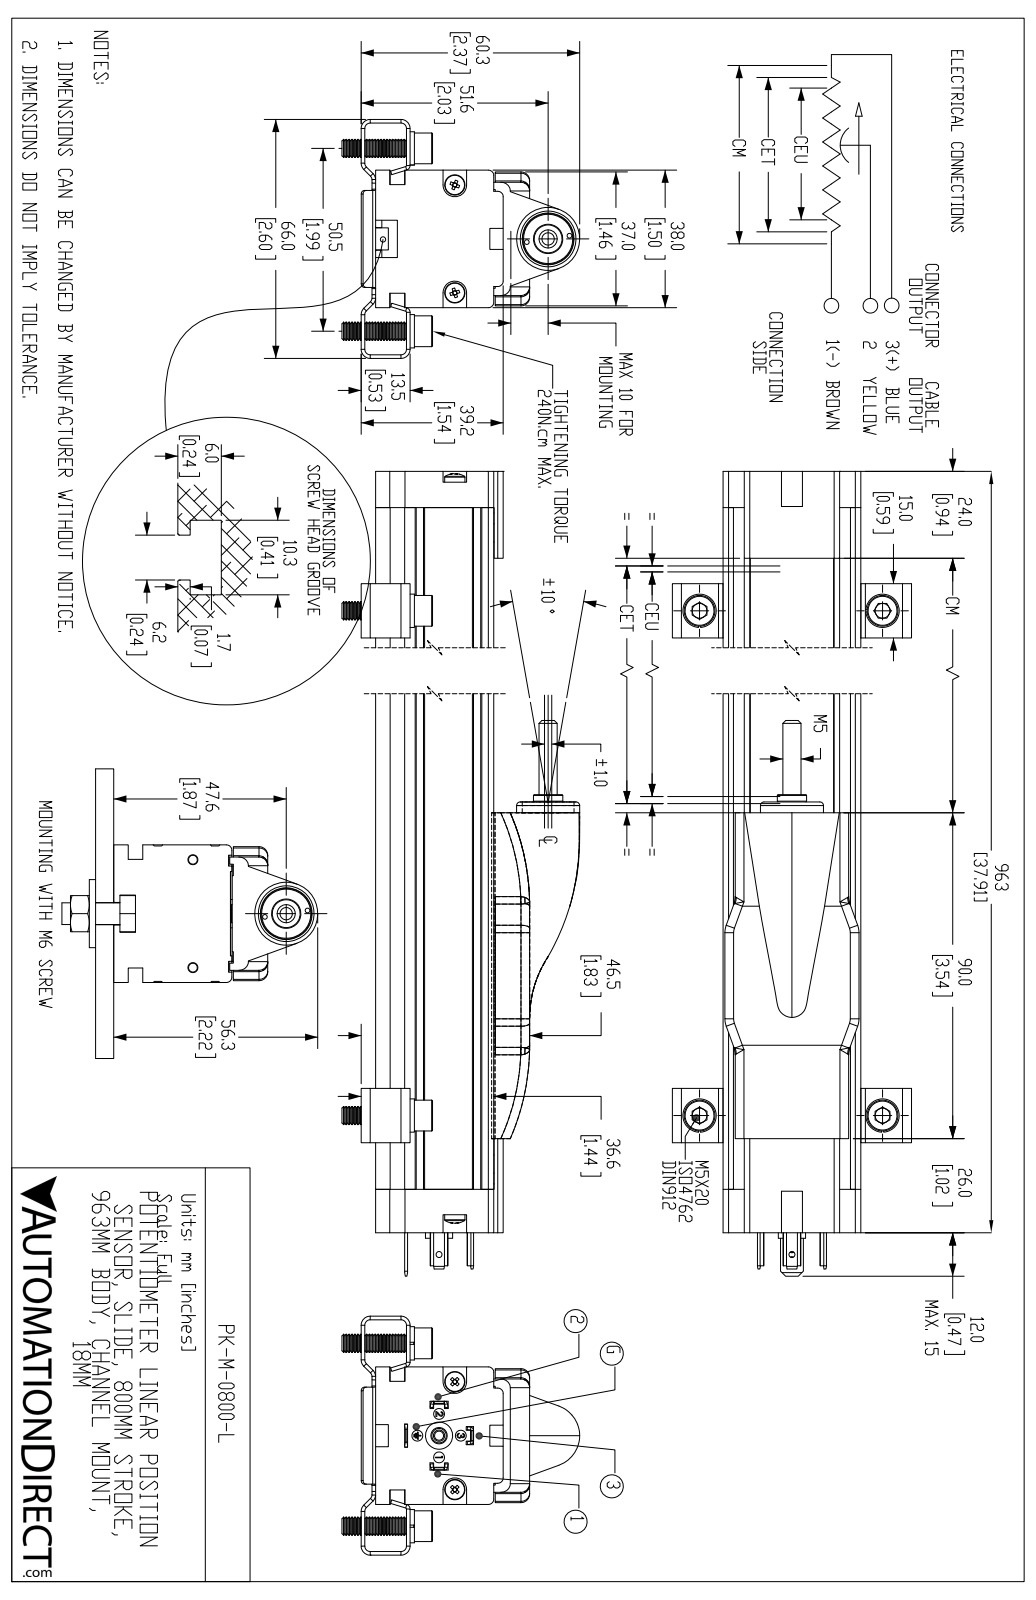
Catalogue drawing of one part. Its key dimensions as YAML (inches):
part_name: "PK-M-0800-L"
step_written_by: "SolidWorks 2019 (AUTOMOTIVE_DESIGN)"
units: inches
bodies: {solids: 27, faces: 1761, planar: 785, cylindrical: 384, other: 592}
overall_size: [38.465, 2.598, 2.583]
volume: 68.86
surface_area: 416.4
round_holes:
  - {diameter: 0.118, count: 5}
  - {diameter: 0.201, count: 4}
  - {diameter: 0.051, count: 2}
  - {diameter: 0.059, count: 2}
  - {diameter: 0.065, count: 2}
  - {diameter: 0.102, count: 2}
  - {diameter: 0.108, count: 2}
  - {diameter: 0.13, count: 2}
  - {diameter: 0.209, count: 2}
  - {diameter: 0.063, count: 1}
  - {diameter: 0.098, count: 1}
  - {diameter: 0.157, count: 1}
round_bosses_or_shafts:
  - {diameter: 0.197, count: 7}
  - {diameter: 0.362, count: 4}
  - {diameter: 0.335, count: 4}
  - {diameter: 0.22, count: 2}
  - {diameter: 0.118, count: 2}
  - {diameter: 0.098, count: 2}
  - {diameter: 0.685, count: 1}
  - {diameter: 0.551, count: 1}
partial_cylinders:
  - {radius: 0.039, count: 28}
  - {radius: 0.059, count: 12}
  - {radius: 0.098, count: 8}
  - {radius: 0.104, count: 8}
  - {radius: 0.236, count: 8}
  - {radius: 0.033, count: 6}
  - {radius: 0.094, count: 6}
  - {radius: 0.024, count: 4}
face_to_face_distances: [1.268, 0.157, 1.272, 1.496, 0.079, 1.035, 0.236, 0.315, 1.031, 0.02]
hole_center_spacings: [0.236, 0.334, 0.234, 0.39, 0.472, 0.484, 0.539, 0.59]
